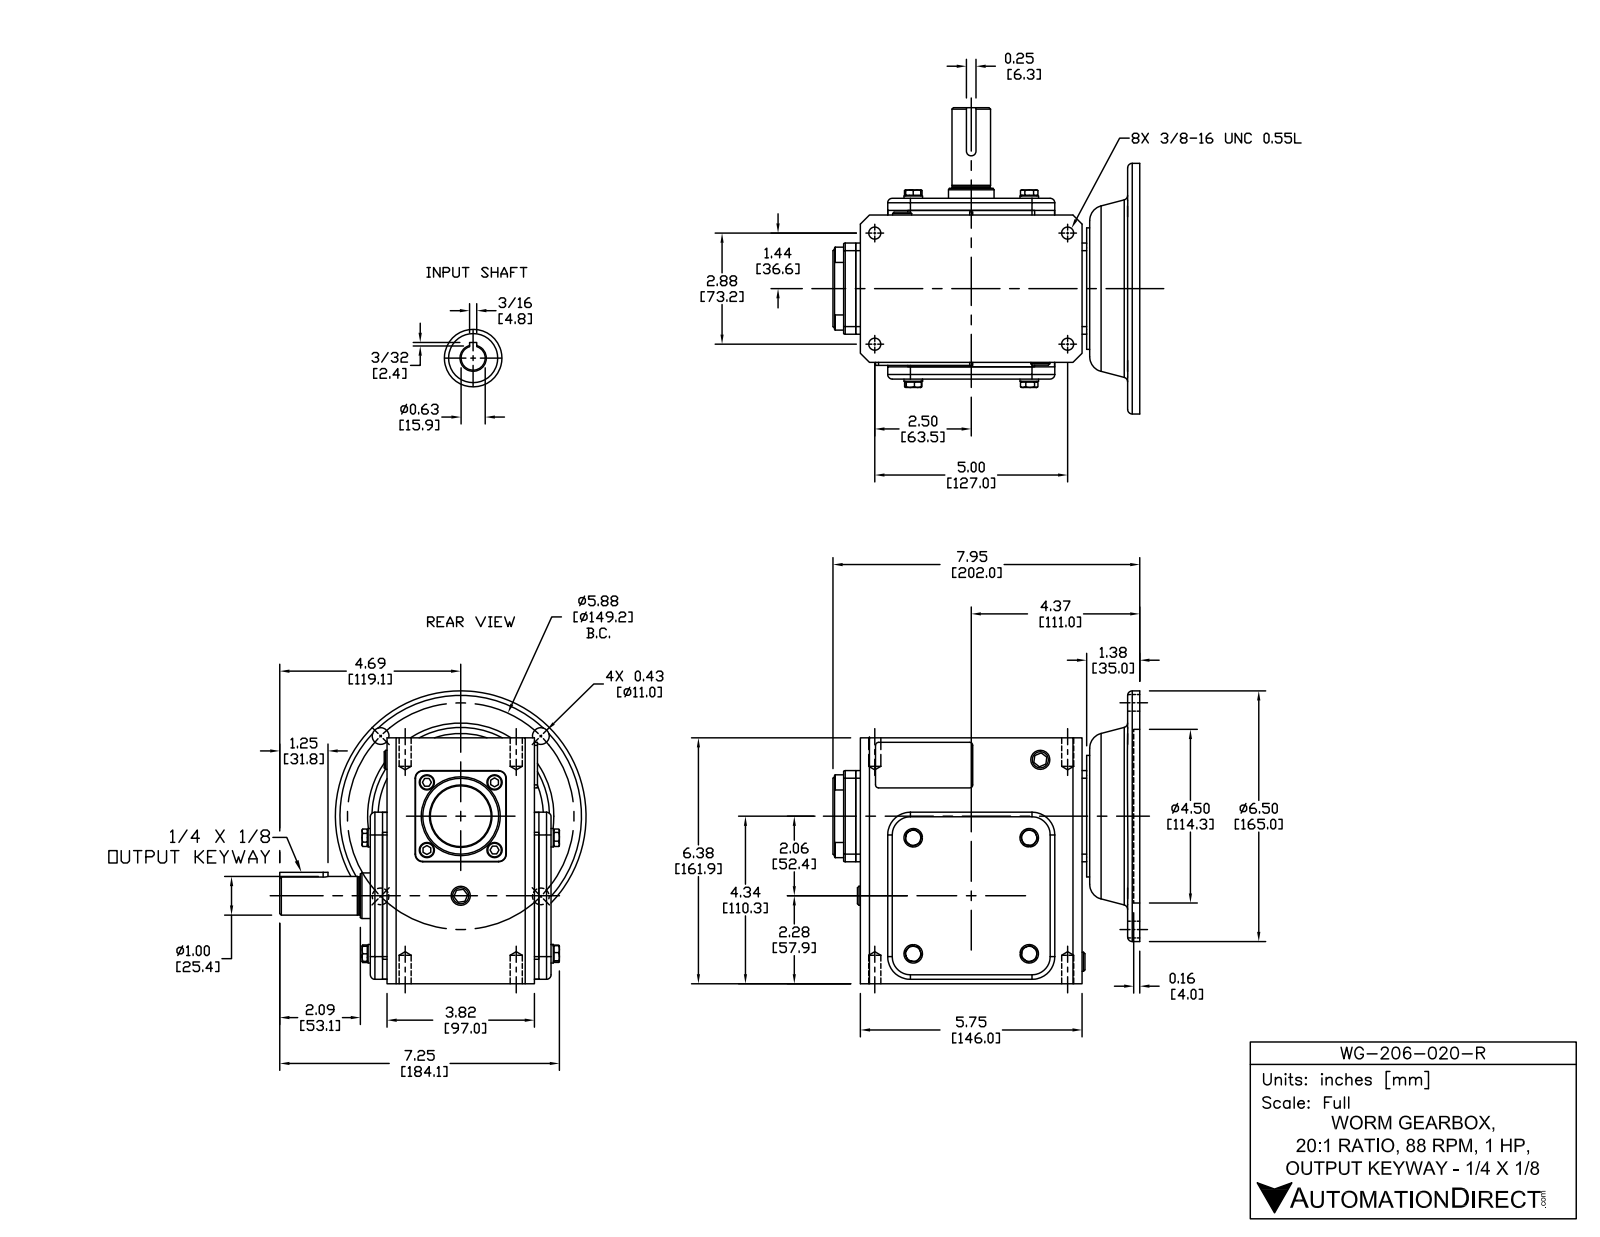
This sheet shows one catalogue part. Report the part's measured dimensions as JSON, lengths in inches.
{"part_name": "WG-206-020-R", "step_written_by": "SolidWorks 2015 (CONFIG_CONTROL_DESIGN)", "units": "inches", "bodies": {"solids": 43, "faces": 610, "planar": 300, "cylindrical": 182, "other": 128}, "overall_size": [7.953, 7.938, 7.591], "volume_in3": 171.8, "surface_area_in2": 407.7, "round_holes": [[0.313, 4], [0.406, 4], [0.591, 1], [0.625, 1], [1.181, 1], [1.457, 1], [1.654, 1], [3.543, 1], [4.5, 1]], "round_bosses_or_shafts": [[0.394, 8], [0.48, 4], [6.496, 1], [3.15, 1], [2.047, 1], [1.575, 1], [1.181, 1], [1.142, 1]], "partial_cylinders_radius": [[0.079, 8], [0.118, 8], [0.197, 4], [0.591, 4], [0.02, 2], [0.039, 2], [0.125, 1], [2.717, 1]], "face_to_face_distances": [0.315, 0.118, 4.055, 4.37, 0.433, 4.252, 3.937, 6.375, 4.685, 0.709], "hole_center_spacings": [2.937, 4.154, 2.077, 2.88, 4.631, 5, 5.77, 5.875]}
